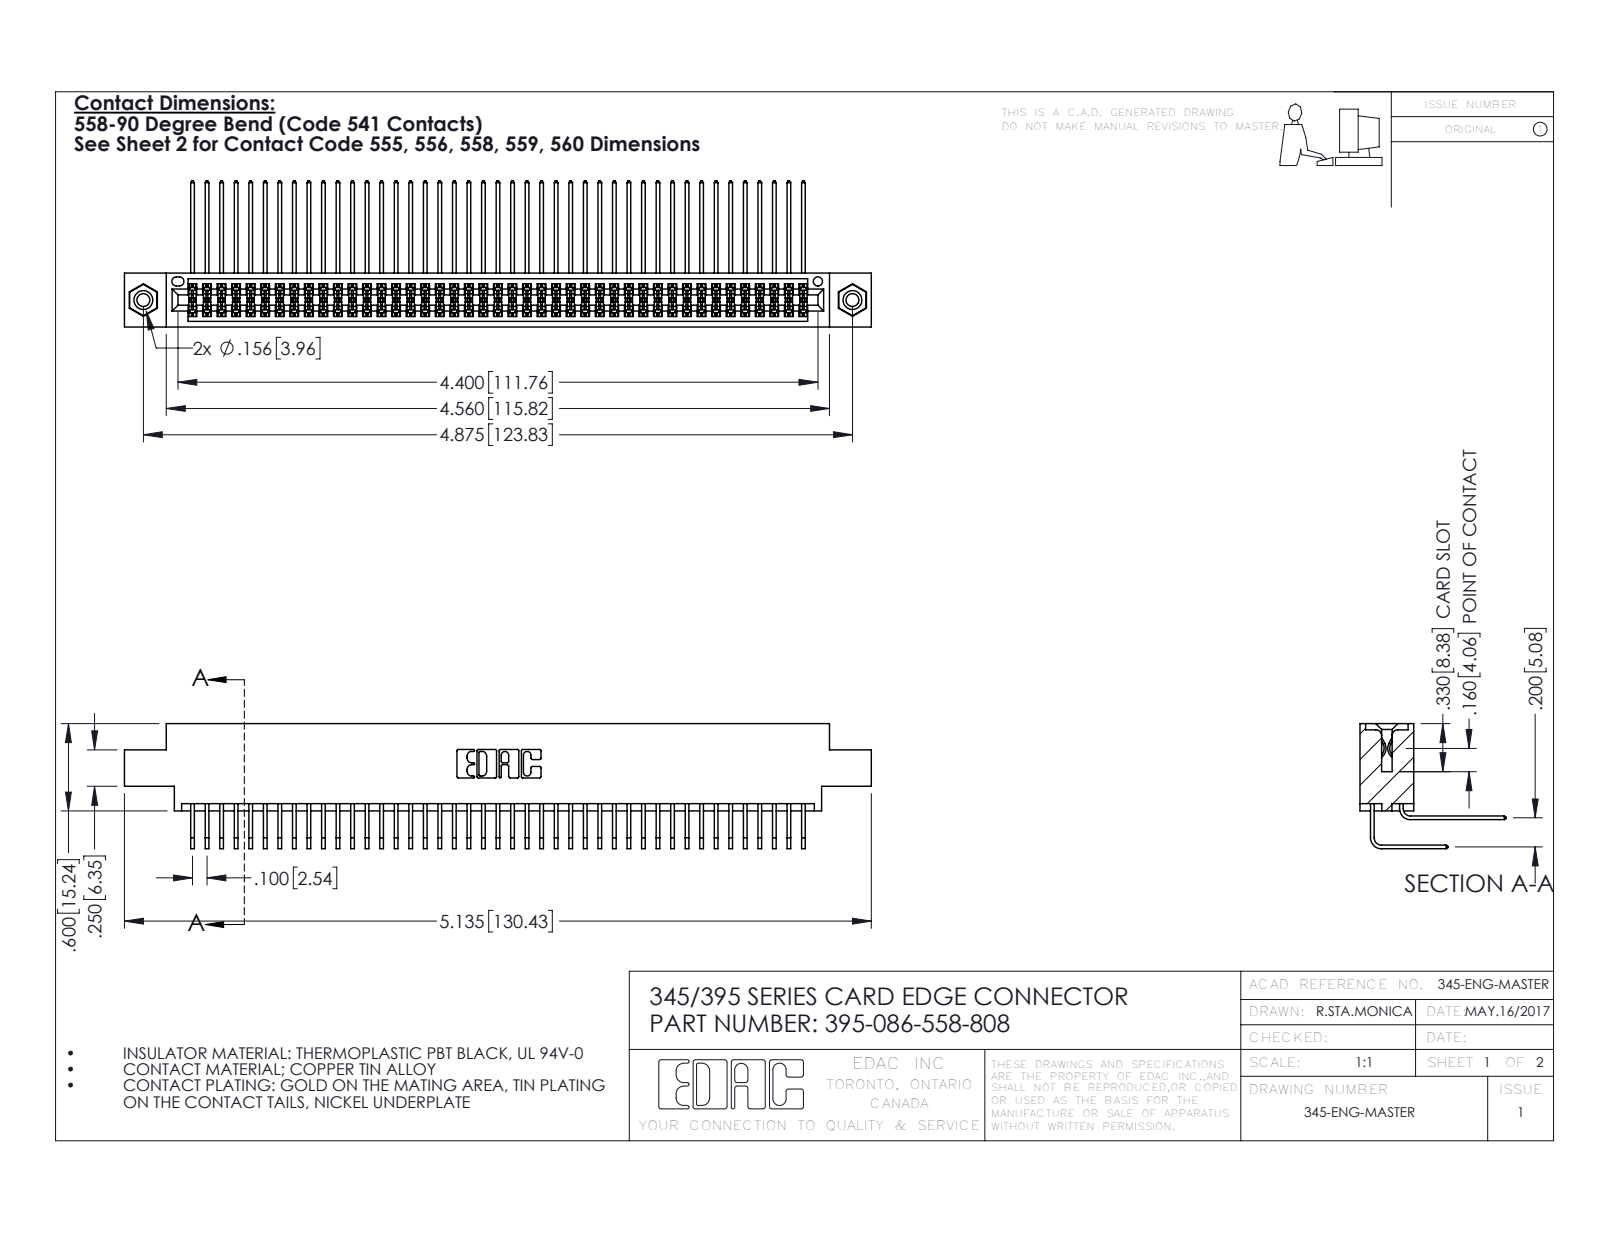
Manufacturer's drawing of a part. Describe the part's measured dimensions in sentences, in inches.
The part is named "345-292-001_558 Tail - 2; 345-250-001_345-250-003-102; 345 Part_0.170 Offset - 0.156 Dia-TI; 395-086-558-808 (+1 more)". Its 3-D file was written by "SolidWorks 2016 (CONFIG_CONTROL_DESIGN)". It is 89 solids with 4662 faces: 3126 planar, 1520 cylindrical and 16 other. Overall it measures 5.135 by 1.005 by 0.859 inches. Its volume is 0.797 cubic inches and its surface area 33.8 square inches. Round holes: 2 of diameter 0.089, 2 of diameter 0.125, 2 of diameter 0.156, 1 of diameter 0.064. Round bosses or shafts: 2 of diameter 0.155. Partial cylindrical surfaces (rounded edges, fillets, slot ends): 130 of radius 0.006, 22 of radius 0.01, 6 of radius 0.007, 6 of radius 0.031, 3 of radius 0.026, 2 of radius 0.014, 2 of radius 0.019, 2 of radius 0.022. The main face-to-face distances are 0.072, 0.298, 0.2, 0.37, 0.098, 0.272, 0.025, 0.225, 0.175, 0.025. The hole center spacings are 0.27, 4.639, 4.875.
